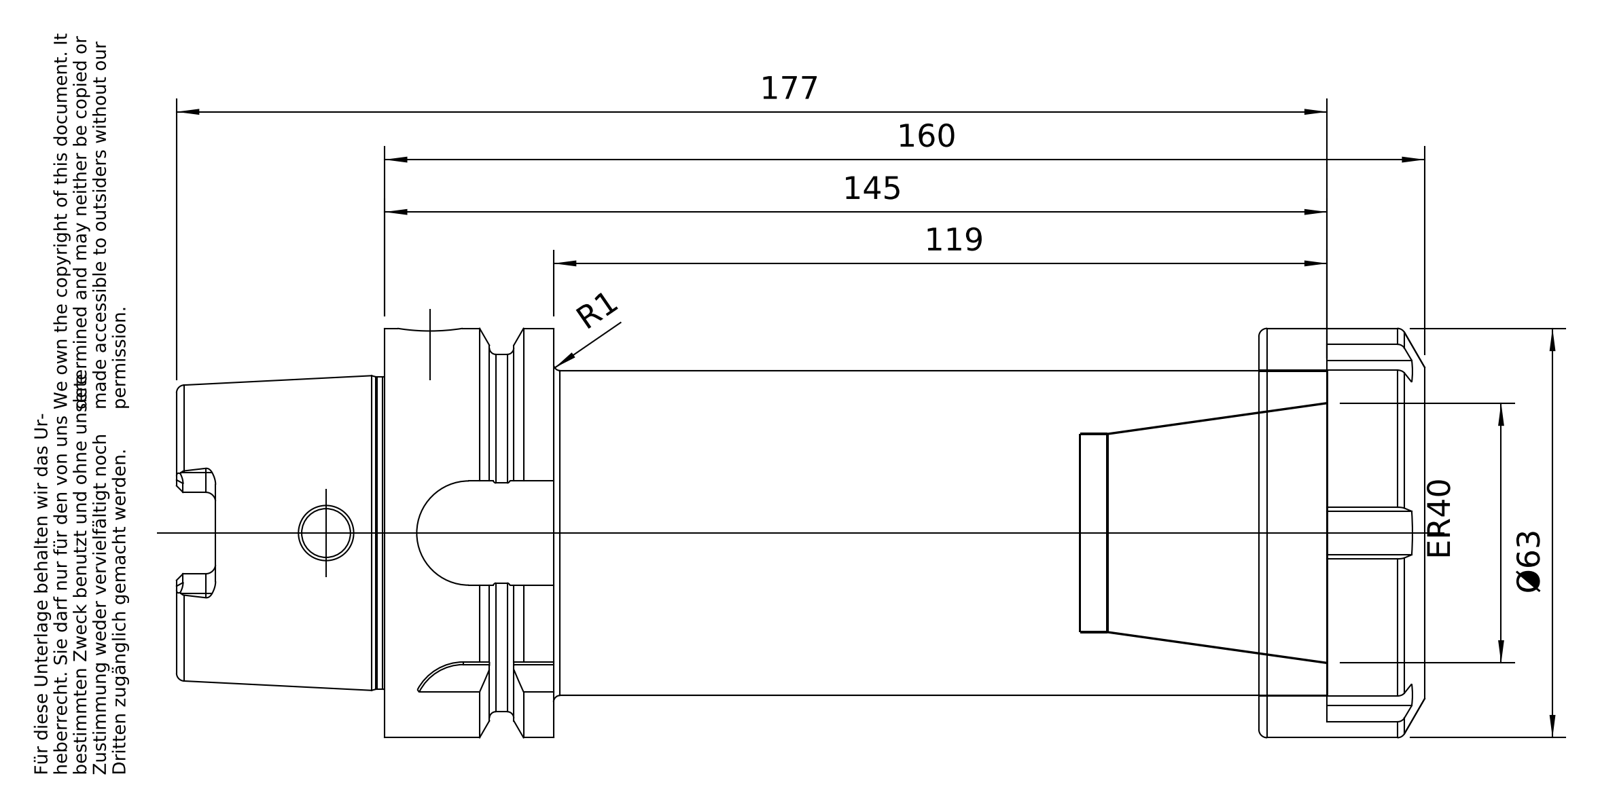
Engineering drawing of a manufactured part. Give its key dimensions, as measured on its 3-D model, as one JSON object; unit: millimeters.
{"part_name": "A63-022-40; 83-912-40; A63-022-40_ASM", "step_written_by": "PRO/ENGINEER BY PARAMETRIC TECHNOLOGY CORPORATION, 2010430 (CONFIG_CONTROL_DESIGN)", "units": "millimeters", "bodies": {"solids": 2, "faces": 217, "planar": 85, "cylindrical": 56, "other": 76}, "overall_size": [192, 63, 63], "volume_mm3": 355001, "surface_area_mm2": 55784, "round_holes": [[7.5, 1], [10, 1], [16.92, 1], [18.32, 1], [18.66, 1], [30.5, 1], [34, 1], [40, 1]], "round_bosses_or_shafts": [[63, 1], [55, 1], [50, 1], [48.04, 1], [18, 1]], "partial_cylinders_radius": [[1.5, 6], [2.7, 6], [3, 4], [8, 1], [8.02, 1], [9.02, 1]], "face_to_face_distances": [25.5, 134.5, 160, 26, 108.5, 134, 107, 81, 27.5, 53]}
